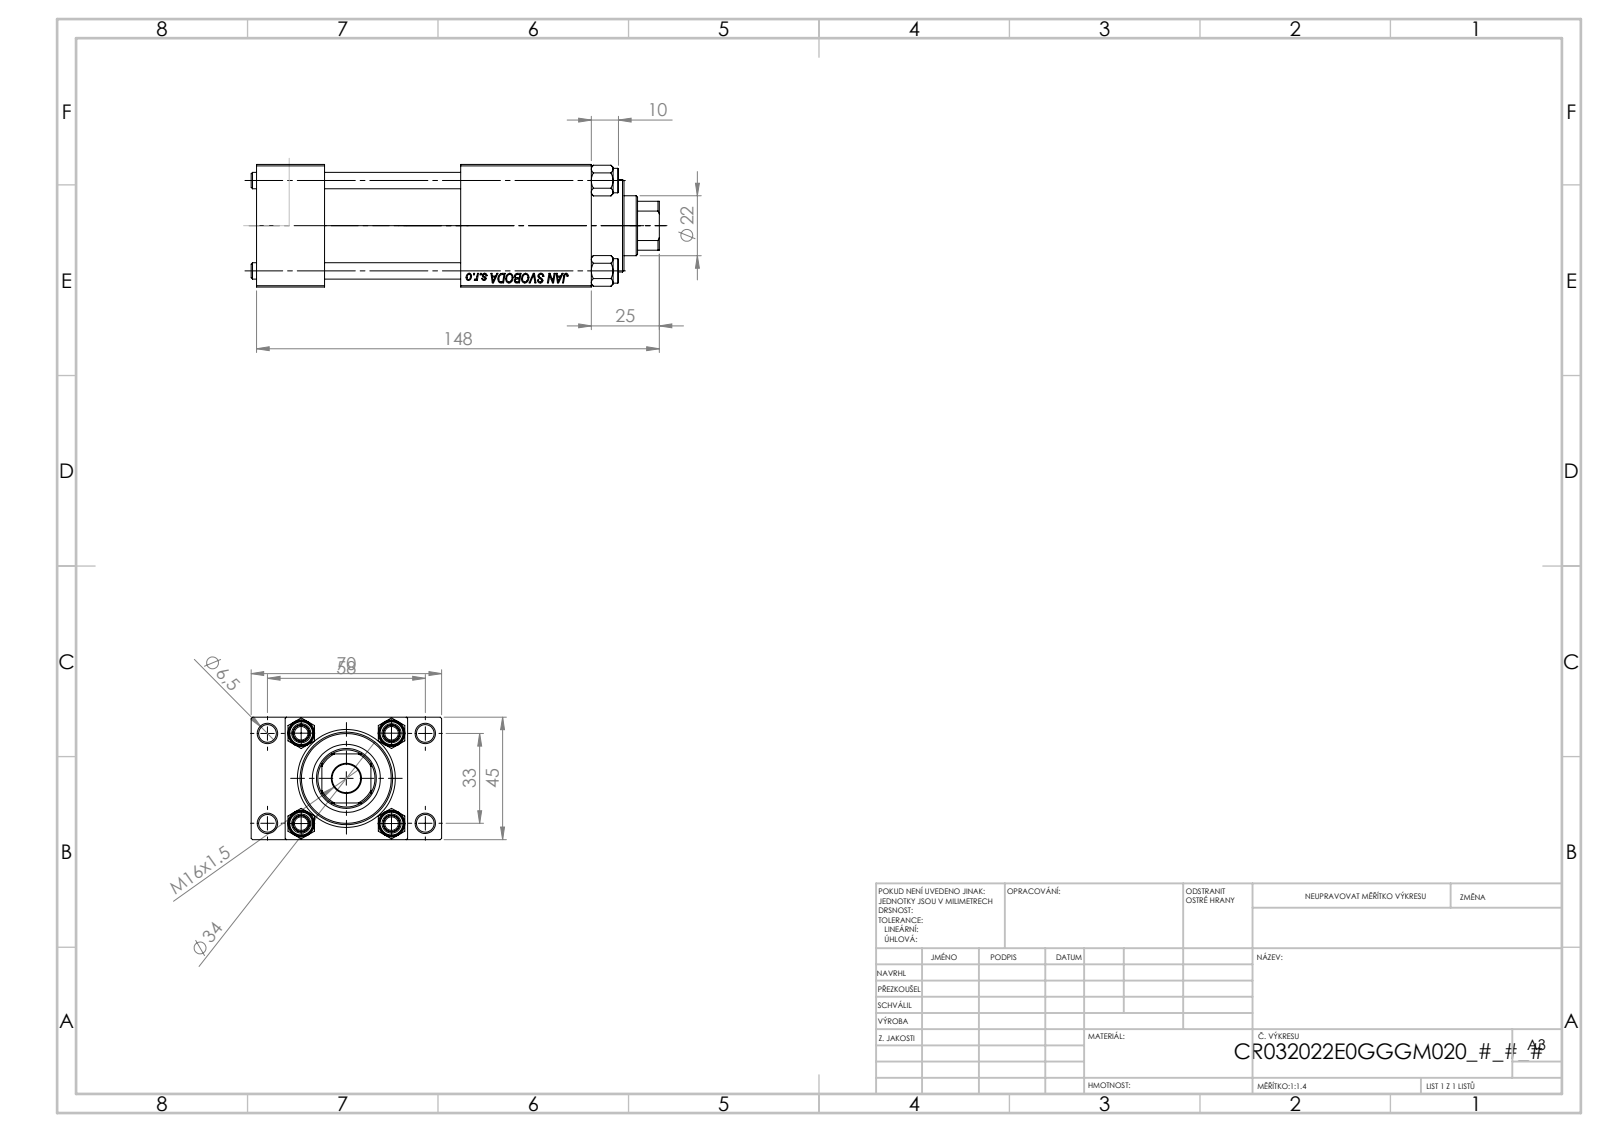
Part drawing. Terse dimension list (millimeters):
name: V215CR_TYCINKA_E; V215CR_E_Body; V215CR_VCP_E; V215_VC_A (+1 more)
written by: SolidWorks 2019 (CONFIG_CONTROL_DESIGN)
unit: mm
bodies: 11 solids, 1136 faces (497 planar, 87 cylindrical, 552 other)
size: 150 × 70 × 45
volume: 236 488 mm³; area: 80 592 mm²
holes: 4× ⌀6, 4× ⌀6.5, 2× ⌀7, 2× ⌀13.16, 2× ⌀20, 1× ⌀10.5, 1× ⌀22, 1× ⌀24, 1× ⌀25, 1× ⌀32, 1× ⌀33
bosses: 4× ⌀9, 1× ⌀38, 1× ⌀34
rounds: 1× R10.5
face distances: 45, 25, 12.5, 57.5, 123, 70, 50, 75, 98, 48
hole spacings: 12.4, 23.48, 33.2, 33.37, 35.35, 45.6, 56.35, 33
